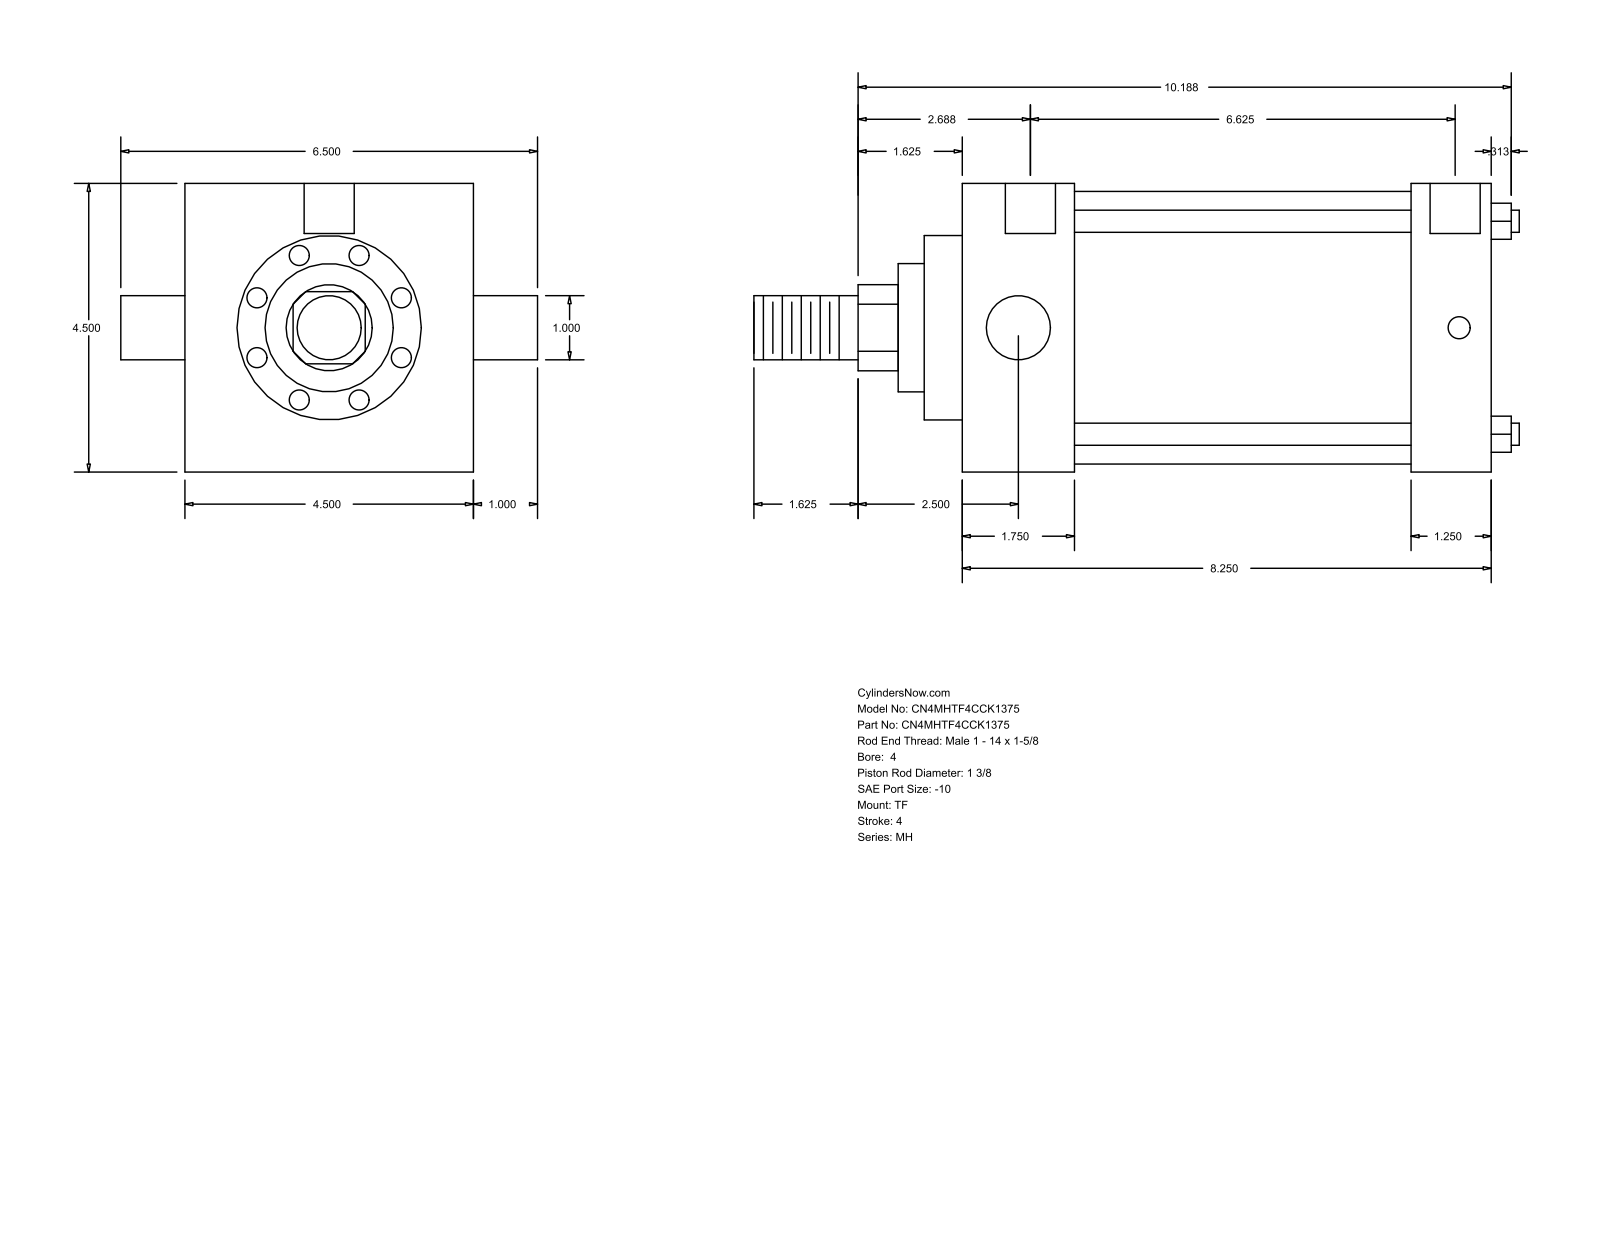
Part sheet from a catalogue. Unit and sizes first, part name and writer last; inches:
Units: inches
Overall size (bounding box): 11.937 × 6.5 × 4.5
Round holes (diameter × count): ⌀0.344 ×3, ⌀0.781 ×2
Round bosses / shafts (diameter × count): ⌀0.345 ×4, ⌀1 ×2, ⌀4.25 ×1, ⌀2.875 ×1, ⌀2 ×1, ⌀1.375 ×1
Partial cylindrical surfaces — rounded edges, fillets, slot ends (radius × count): R0.672 ×1
Main face-to-face distances: 4.5, 8.25, 6.5, 1.75, 7, 5.25, 1.25, 0.594, 2.344, 7.594
Hole centre spacings: 0.062, 0.063, 6.625, 6.687, 6.688, 6.75
Bodies: 0 solids, 86 faces (61 planar, 25 cylindrical, 0 other)
Part name (STEP PRODUCT): MH_TF__0400_1.375
STEP written by: GSSL Pune (CONFIG_CONTROL_DESIGN)
